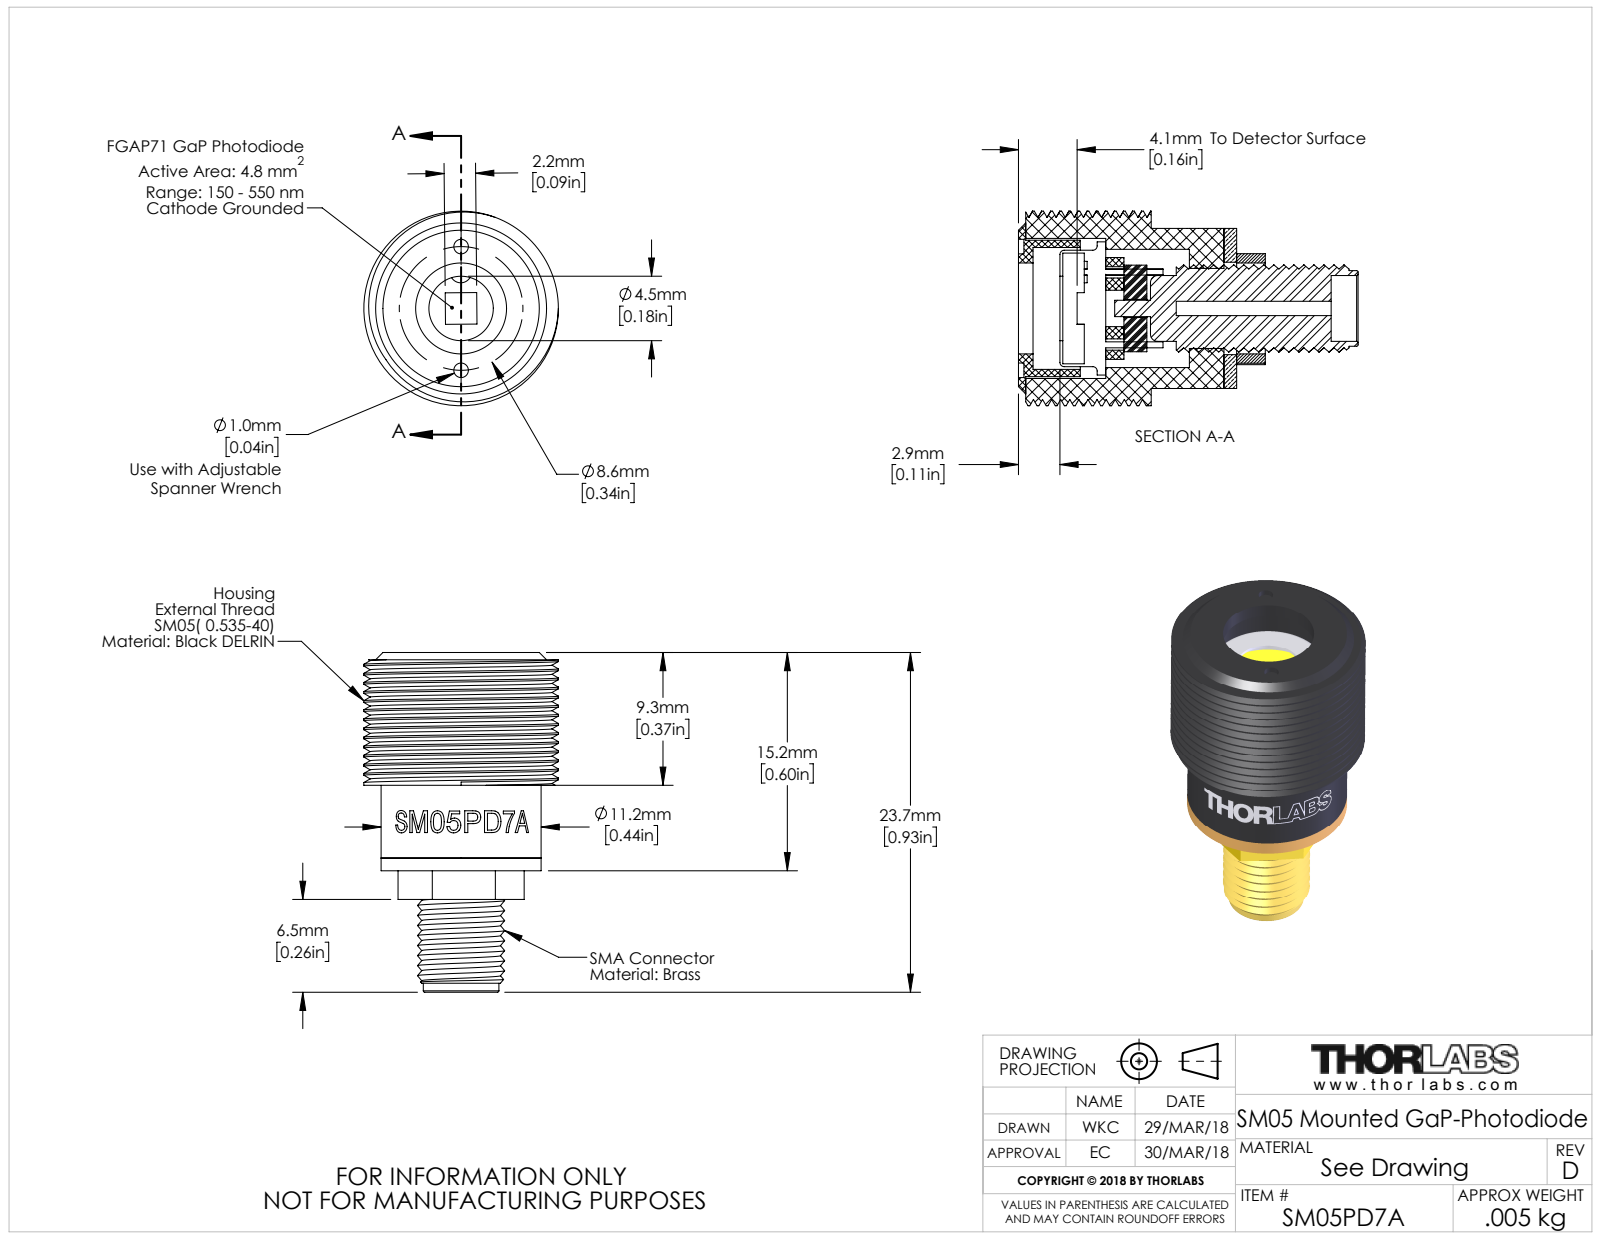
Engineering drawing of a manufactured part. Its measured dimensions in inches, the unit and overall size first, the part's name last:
Units: inches
Overall size (bounding box): 0.924 × 0.535 × 0.535
Round holes (diameter × count): ⌀0.04 ×2, ⌀0.039 ×1, ⌀0.059 ×1, ⌀0.177 ×1, ⌀0.181 ×1, ⌀0.22 ×1, ⌀0.25 ×1, ⌀0.254 ×1, ⌀0.304 ×1, ⌀0.325 ×1, ⌀0.335 ×1, ⌀0.385 ×1
Round bosses / shafts (diameter × count): ⌀0.017 ×2, ⌀0.535 ×1, ⌀0.44 ×1, ⌀0.375 ×1, ⌀0.366 ×1, ⌀0.32 ×1, ⌀0.208 ×1, ⌀0.045 ×1
Main face-to-face distances: 0.335, 0.02, 0.035, 0.37, 0.059, 0.58, 0.545, 0.21, 0.6, 0.565
Hole centre spacings: 0.17, 0.07, 0.1, 0.27, 0.34
Volume: 0.091 in³ · Surface area: 4.364 in²
Bodies: 6 solids, 112 faces (46 planar, 51 cylindrical, 15 other)
Part name (STEP PRODUCT): 12054-E0W
STEP written by: SolidWorks 2016 (AUTOMOTIVE_DESIGN)
